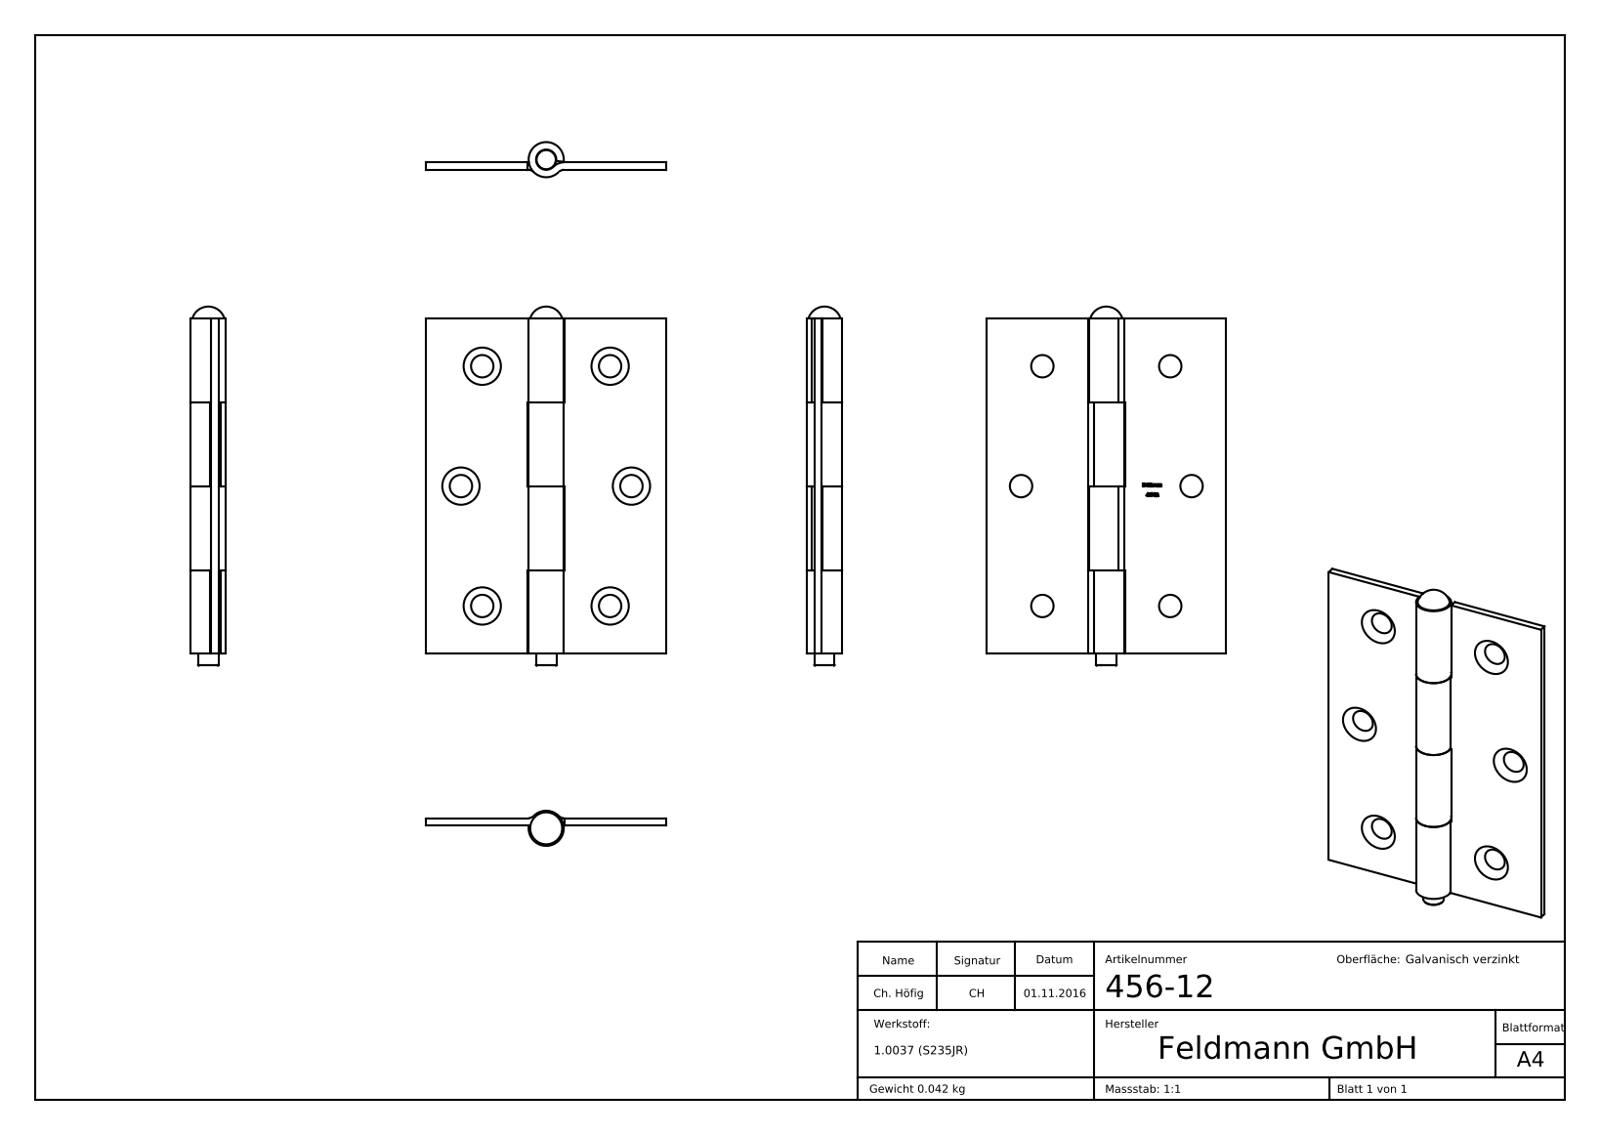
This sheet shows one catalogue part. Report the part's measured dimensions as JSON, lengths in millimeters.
{"part_name": "456-12; 456-12 Teil2; 456-12 Teil1; 456-12 Teil3", "step_written_by": "SolidWorks 2018 (CONFIG_CONTROL_DESIGN)", "units": "millimeters", "bodies": {"solids": 3, "faces": 233, "planar": 137, "cylindrical": 17, "other": 79}, "overall_size": [67.4, 45, 6.6], "volume_mm3": 5367, "surface_area_mm2": 8251, "round_holes": [[3.8, 1]], "round_bosses_or_shafts": [[6.6, 1]], "partial_cylinders_radius": [[1.4, 2], [2.8, 2]], "face_to_face_distances": [1.4, 15.75, 31.5, 47.25, 19, 26, 45, 63, 7, 2.2]}
